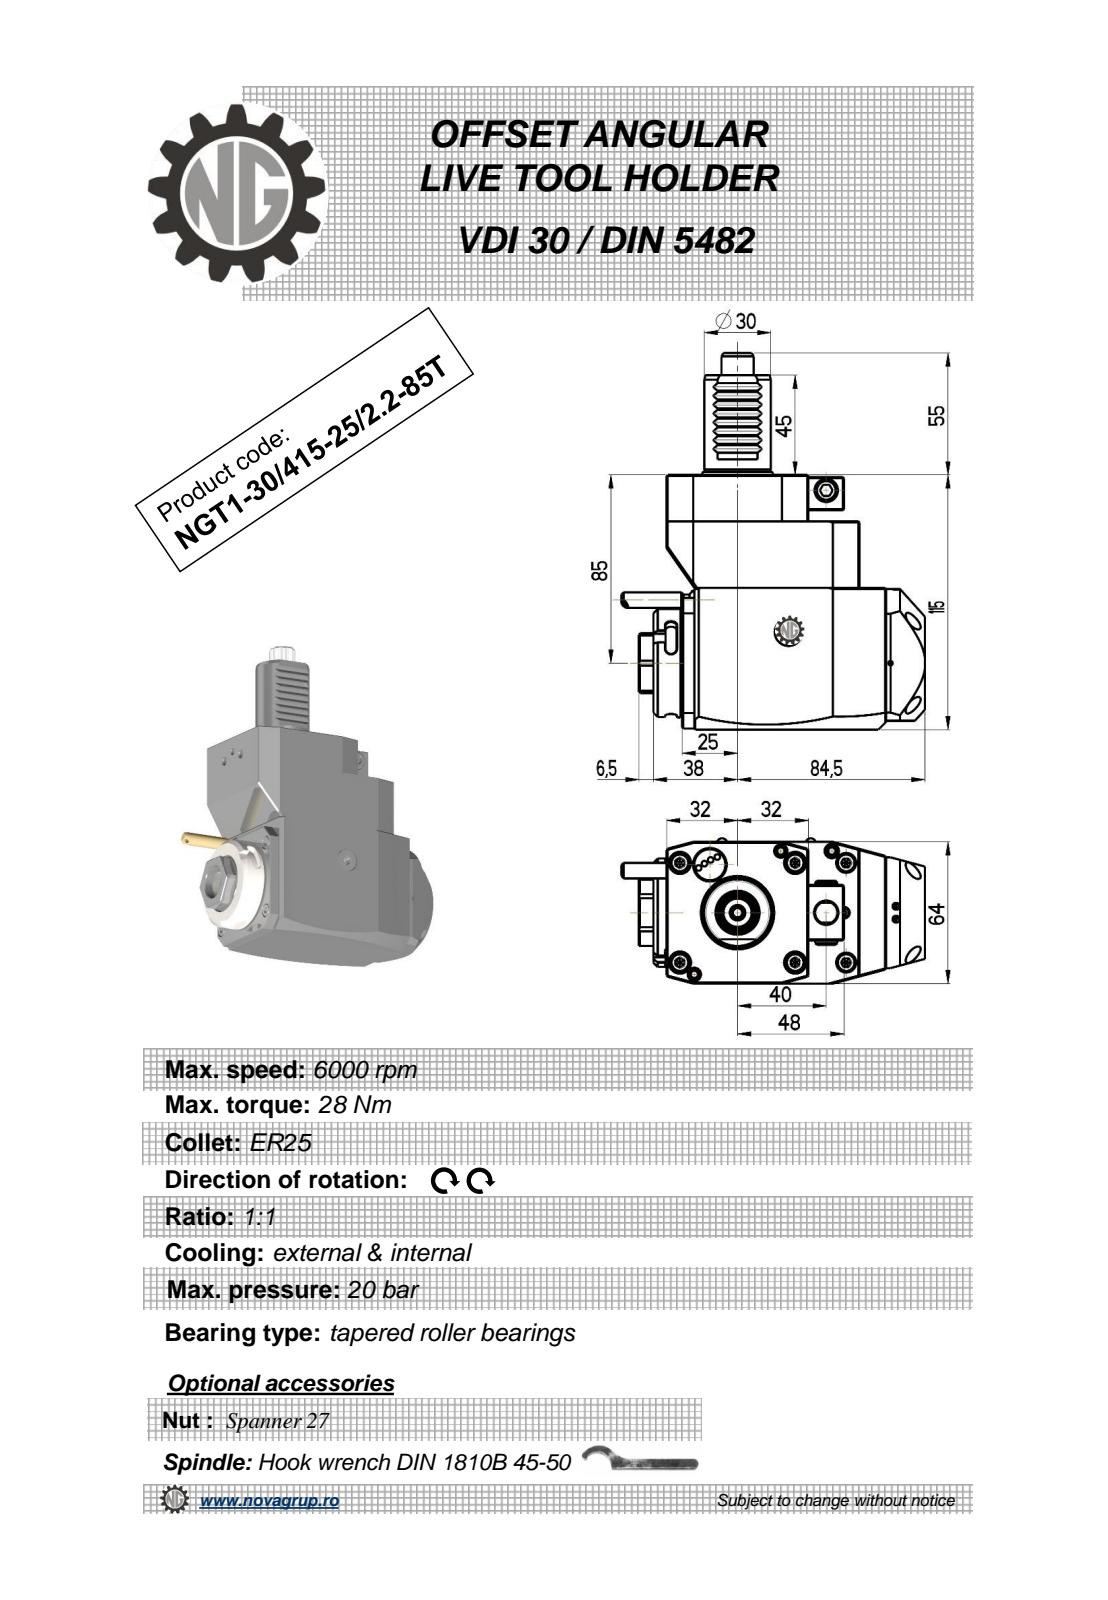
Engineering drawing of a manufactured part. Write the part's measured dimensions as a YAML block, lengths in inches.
part_name: "NGT1_30_415_25_1_2_85T"
step_written_by: "PRO/ENGINEER BY PARAMETRIC TECHNOLOGY CORPORATION, 2010280 (CONFIG_CONTROL_DESIGN)"
units: inches
bodies: {solids: 1, faces: 364, planar: 178, cylindrical: 100, other: 86}
overall_size: [6.693, 5.389, 2.52]
volume: 43.05
surface_area: 90.95
round_holes:
  - {diameter: 0.098, count: 1}
  - {diameter: 0.118, count: 1}
  - {diameter: 0.165, count: 1}
  - {diameter: 0.209, count: 1}
  - {diameter: 0.335, count: 1}
  - {diameter: 0.374, count: 1}
  - {diameter: 0.394, count: 1}
  - {diameter: 0.709, count: 1}
round_bosses_or_shafts:
  - {diameter: 0.353, count: 2}
  - {diameter: 1.929, count: 1}
  - {diameter: 1.654, count: 1}
  - {diameter: 1.181, count: 1}
  - {diameter: 0.394, count: 1}
  - {diameter: 0.276, count: 1}
  - {diameter: 0.197, count: 1}
partial_cylinders:
  - {radius: 0.115, count: 16}
  - {radius: 0.012, count: 8}
  - {radius: 0.098, count: 6}
  - {radius: 7.087, count: 2}
  - {radius: 0.177, count: 1}
  - {radius: 0.226, count: 1}
  - {radius: 0.285, count: 1}
  - {radius: 0.591, count: 1}
face_to_face_distances: [2.52, 4.528, 0.276, 3.15, 3.425, 0.236, 3.701, 0.827, 4.587, 1.161]
hole_center_spacings: [1.348, 1.575, 2.032, 3.012]
